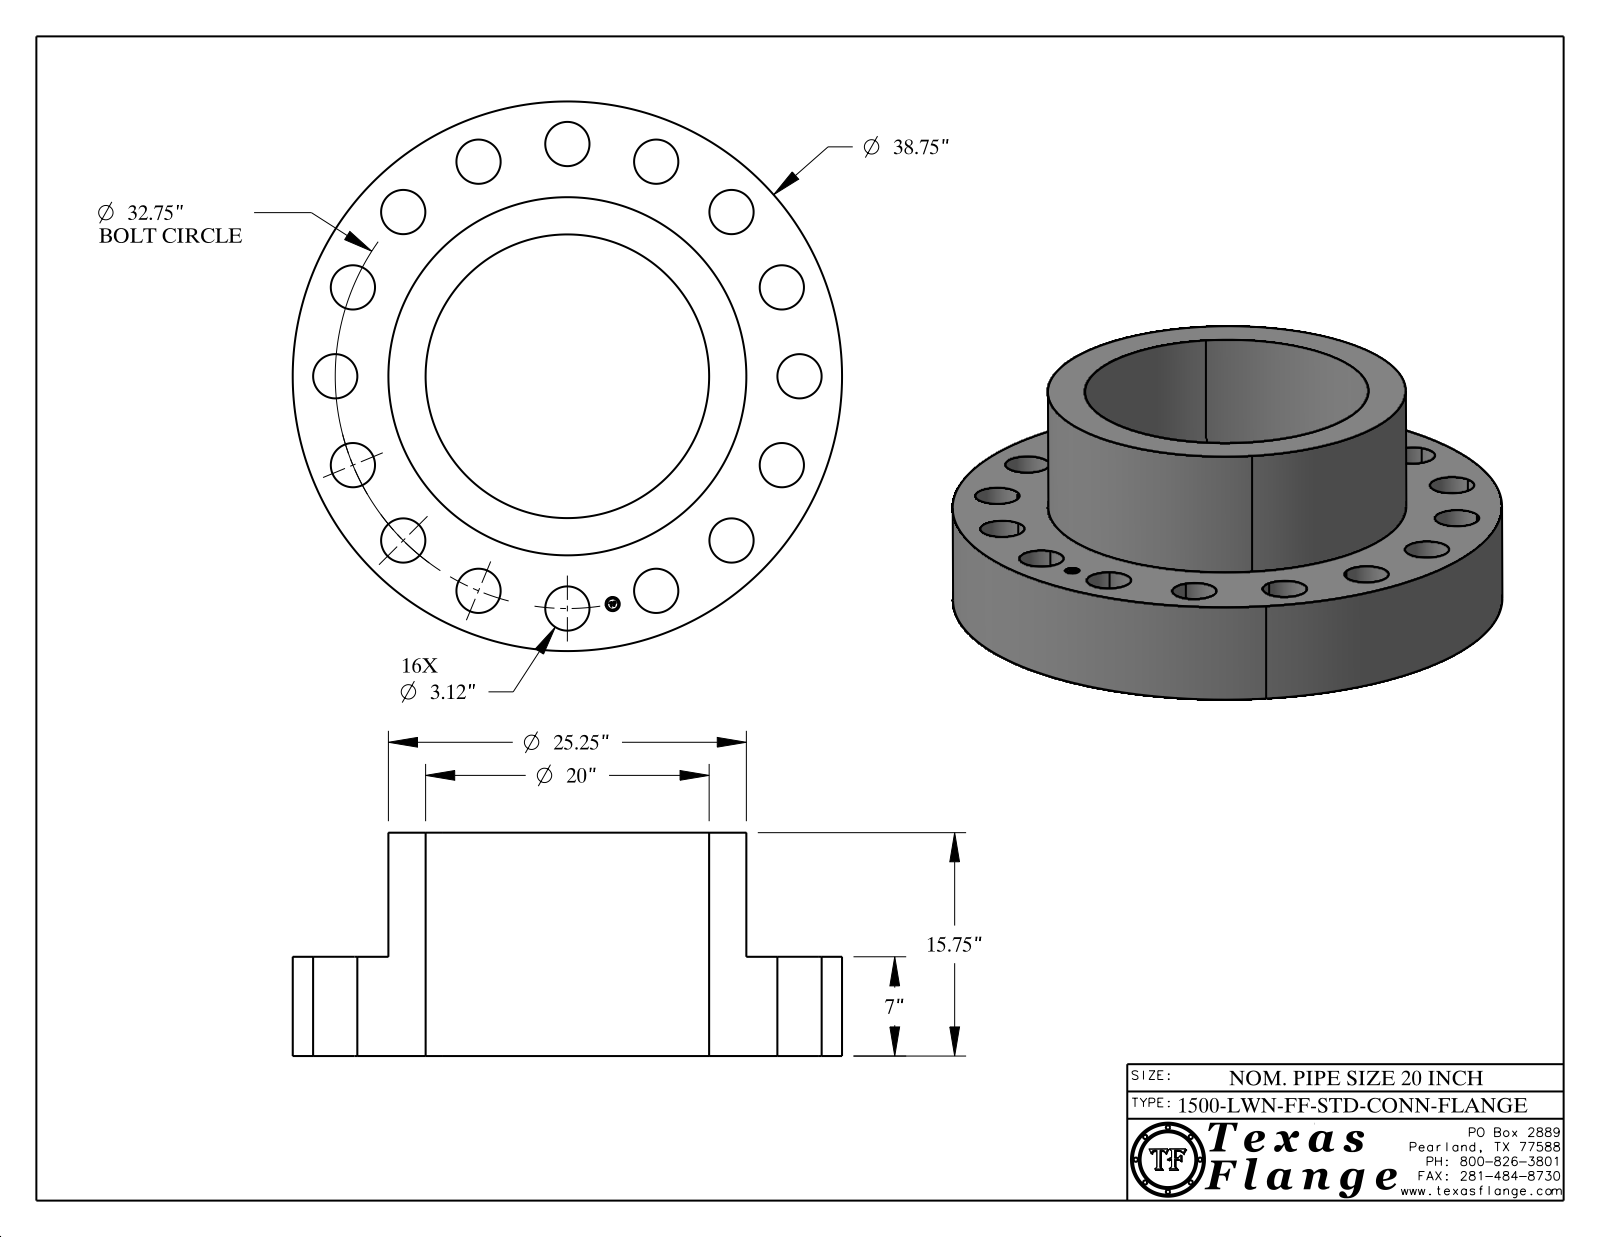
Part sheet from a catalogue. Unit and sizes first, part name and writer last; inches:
Units: inches
Overall size (bounding box): 38.75 × 38.75 × 15.75
Round holes (diameter × count): ⌀3.12 ×16, ⌀1 ×1, ⌀20 ×1
Round bosses / shafts (diameter × count): ⌀0.061 ×8, ⌀38.75 ×1, ⌀25.25 ×1, ⌀0.788 ×1
Main face-to-face distances: 7, 15.75, 8.75, 6.995, 8.755, 0.298, 0.292, 0.055, 0.193, 0.248
Hole centre spacings: 18.195, 16.375, 12.533, 23.157, 30.257, 6.389, 6.389, 27.23
Volume: 6 832 in³ · Surface area: 5 119 in²
Bodies: 1 solid, 426 faces (368 planar, 58 cylindrical, 0 other)
Part name (STEP PRODUCT): 20-1500-LWN-FF-STD-CONN-FLANGE
STEP written by: CATIA V5 STEP AP214 (AUTOMOTIVE_DESIGN)
